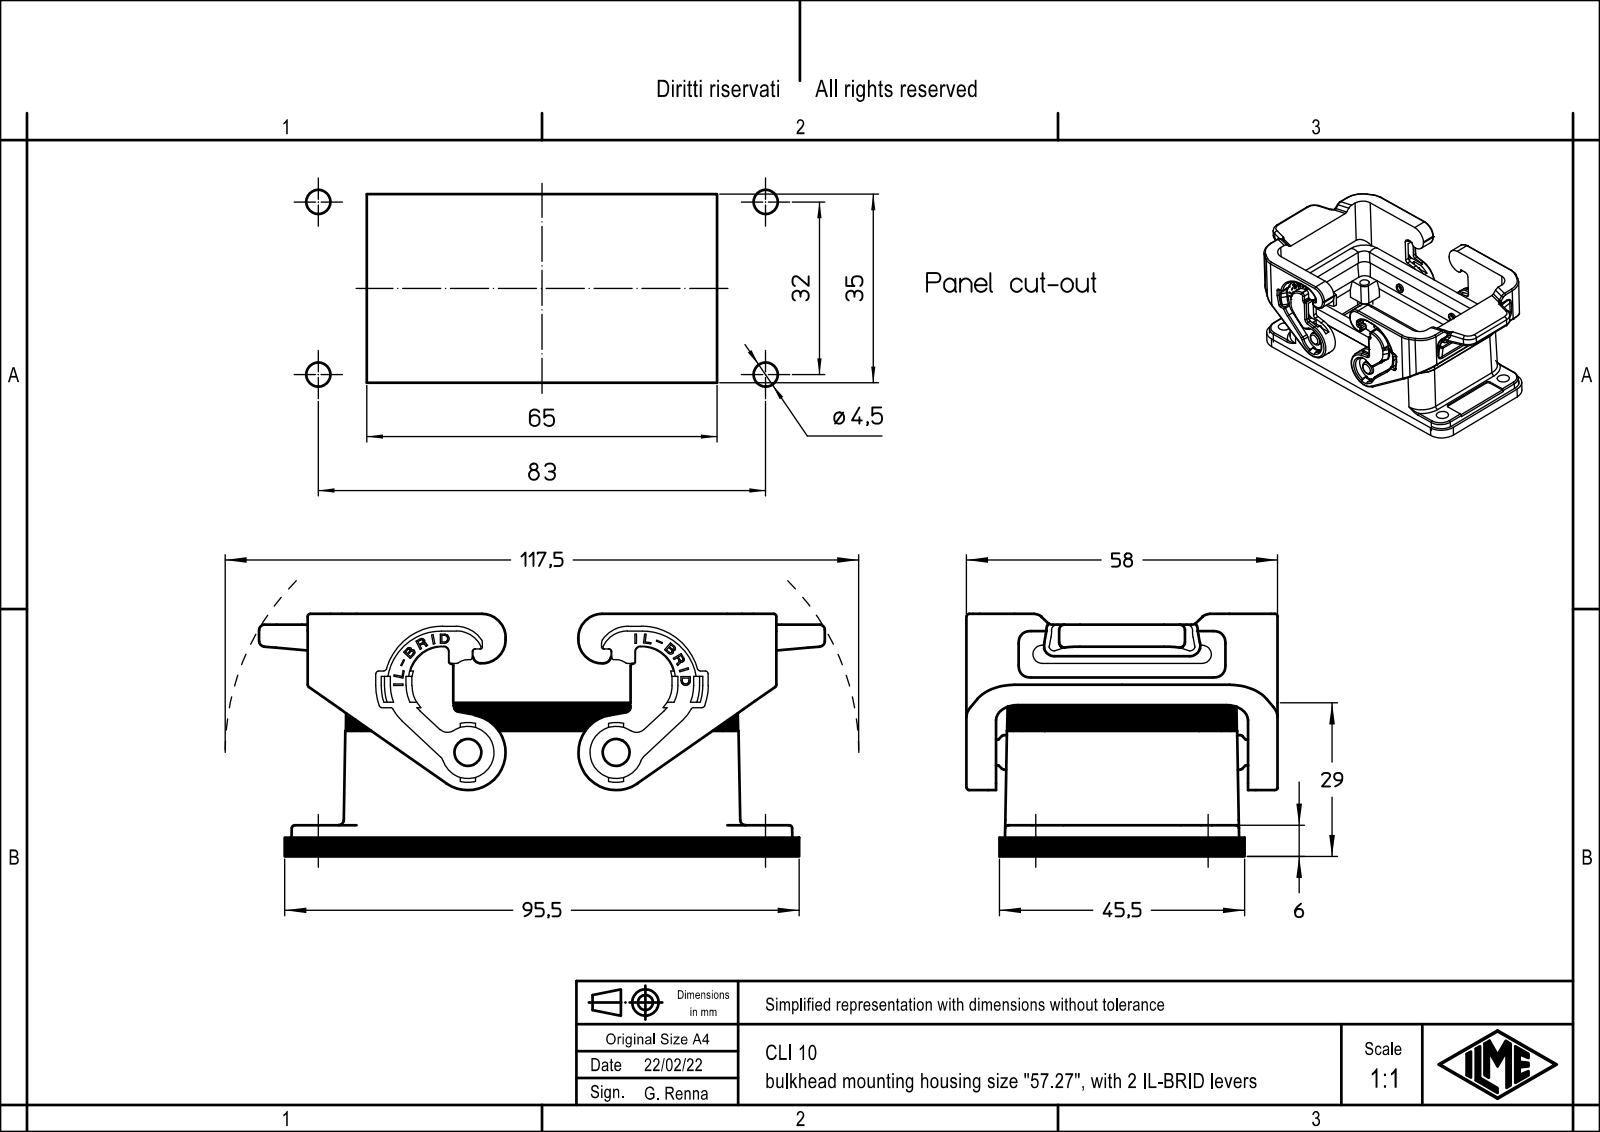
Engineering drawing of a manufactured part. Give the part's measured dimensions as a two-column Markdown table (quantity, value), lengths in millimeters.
| quantity | value |
| --- | --- |
| part name | CLI_10 |
| STEP written by | Creo Elements/Direct Modeling 20.1B 02-Apr-2019 (C) Parametric Technology GmbH (AUTOMOTIVE_DESIGN) |
| units | millimeters |
| bodies | 1 solid, 1236 faces (895 planar, 283 cylindrical, 58 other) |
| overall size | 105 × 58 × 45 |
| volume | 51 276 mm³ |
| surface area | 32 194 mm² |
| round holes (diameter × count) | 2.75 × 4, 3.8 × 4, 4.9 × 4 |
| round bosses / shafts (diameter × count) | 6.4 × 2, 4.8 × 2 |
| partial cylindrical surfaces (radius × count) | 1 × 32, 3 × 16, 0.17 × 15, 2 × 12, 4 × 12, 0.3 × 8, 6 × 8, 7 × 8 |
| main face-to-face distances | 2, 45, 5, 43, 3.9, 5.5, 7.5, 50.5, 52.5, 3 |
| hole center spacings | 13.24, 32.24, 70.04, 75.96, 27, 32, 57, 63.07 |
